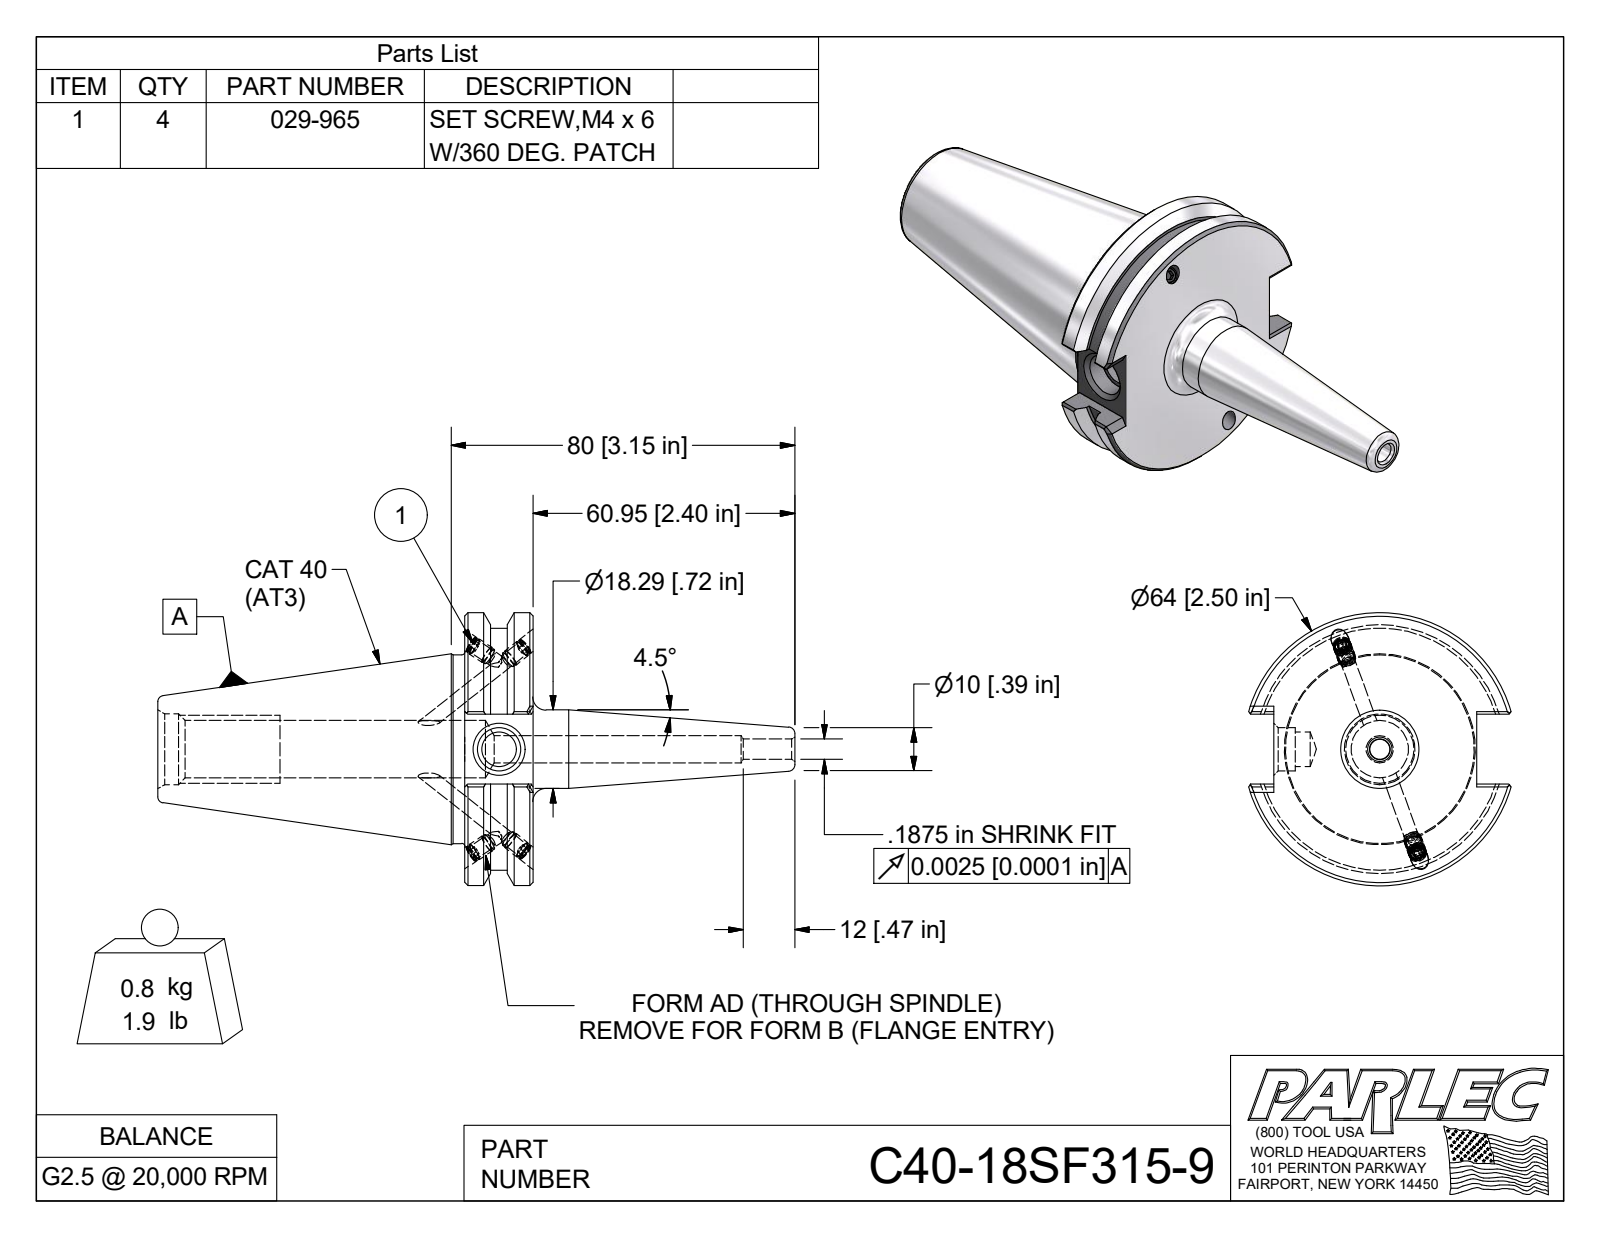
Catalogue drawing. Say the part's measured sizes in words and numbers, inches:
The part is named "C40-18SF315-9; C40BC-18SF315-9-1; 029-965". Its 3-D file was written by "Autodesk Inventor 2009 (AUTOMOTIVE_DESIGN)". It is 5 solids with 150 faces: 76 planar, 29 cylindrical and 45 other. Overall it measures 5.837 by 2.5 by 2.403 inches. Its volume is 6.715 cubic inches and its surface area 38.87 square inches. Round holes: 4 of diameter 0.13, 4 of diameter 0.161, 1 of diameter 0.187. Round bosses or shafts: 4 of diameter 0.165, 4 of diameter 0.157, 1 of diameter 2.5, 1 of diameter 2.219, 1 of diameter 1.73, 1 of diameter 0.72. The main face-to-face distances are 0.625, 0.64, 1.86, 2.812, 3.437, 3.201, 0.389, 0.236, 3.05, 0.238.
